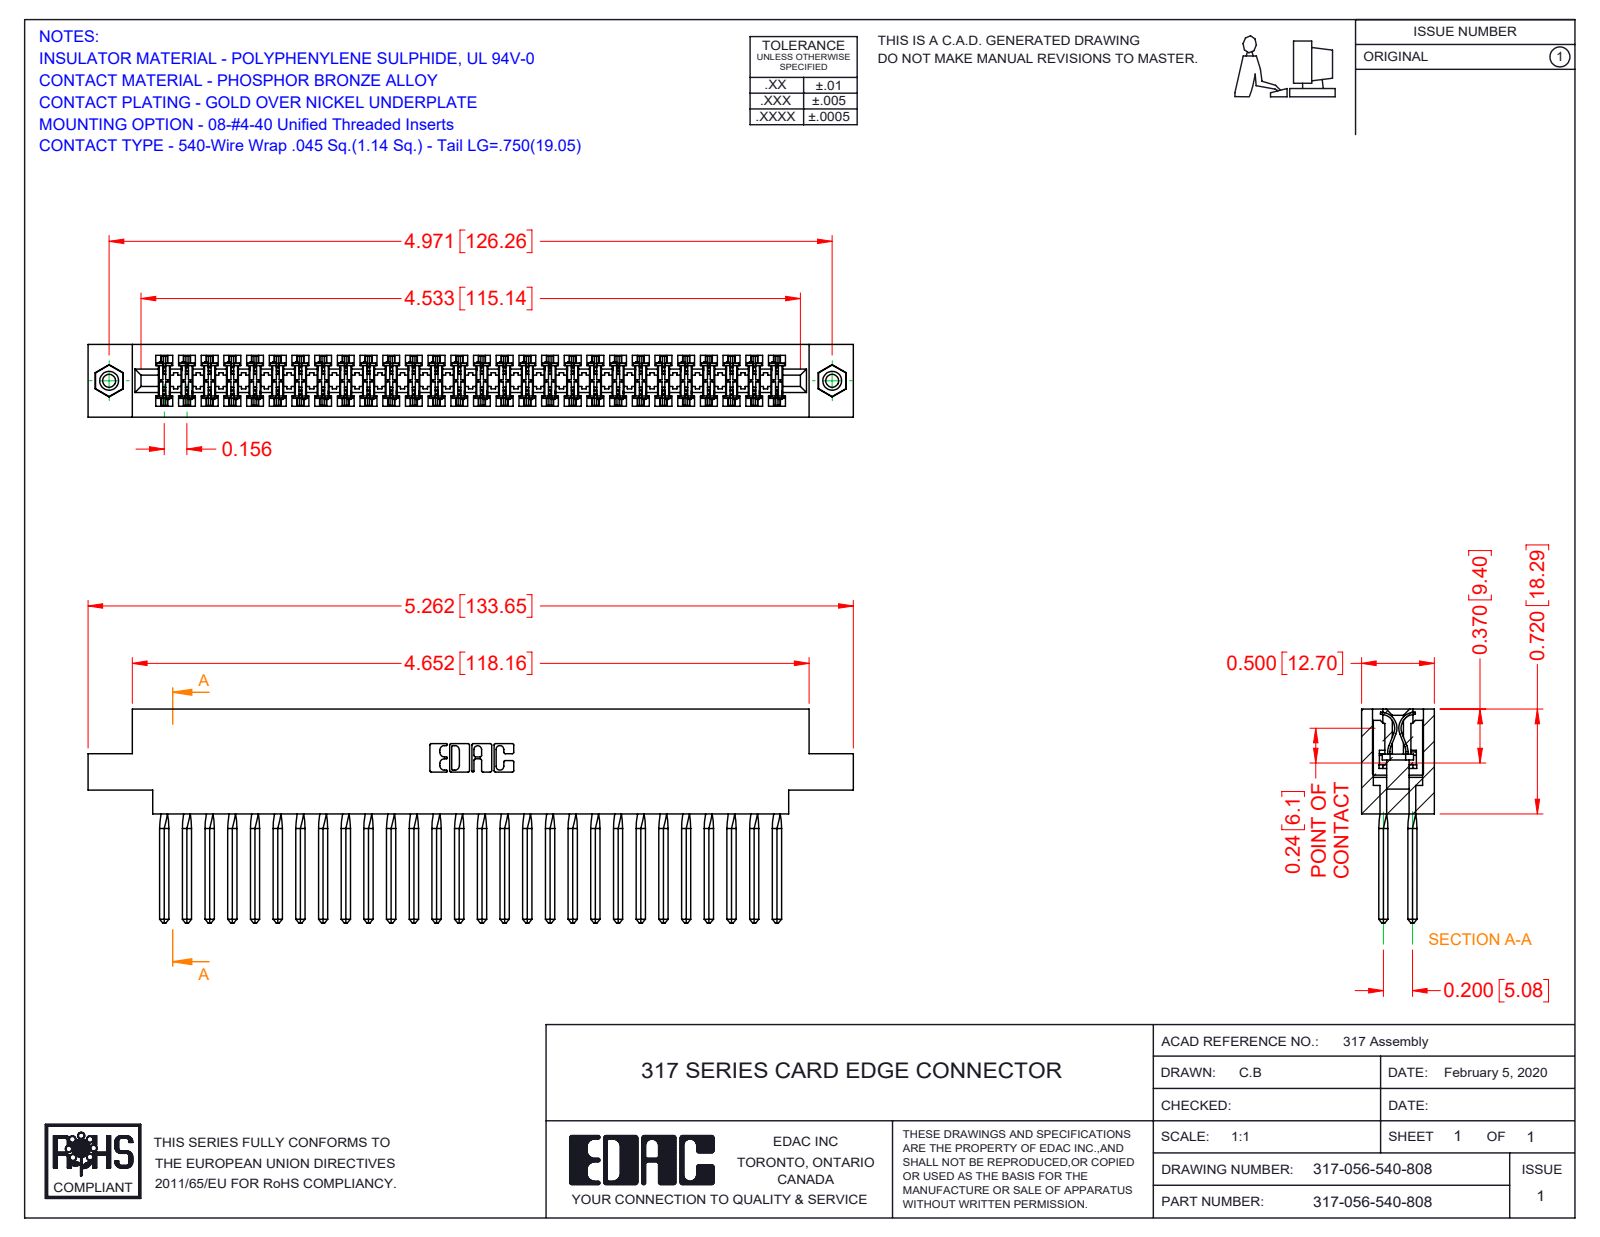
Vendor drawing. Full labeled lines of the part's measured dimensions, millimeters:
Part name (STEP PRODUCT): 317 Part_.156 Dia - TI; 317-290-001_540; 345-250-001_345-250-003-102; 317-056-540-808
STEP written by: SolidWorks 2016 (CONFIG_CONTROL_DESIGN)
Units: millimetres
Bodies: 59 solids, 5146 faces (4178 planar, 728 cylindrical, 240 other)
Overall size (bounding box): 133.7 × 37.3 × 12.7
Volume: 21 960 mm³ · Surface area: 32 220 mm²
Round holes (diameter × count): ⌀2.3 ×2, ⌀3.2 ×2, ⌀4 ×2
Round bosses / shafts (diameter × count): ⌀3.9 ×2
Partial cylindrical surfaces — rounded edges, fillets, slot ends (radius × count): R0.4 ×112, R0.3 ×22, R0.2 ×6, R0.8 ×6, R0.7 ×3, R2.4 ×2, R2.5 ×2, R2.8 ×2
Main face-to-face distances: 12.7, 1.9, 10.8, 8.9, 2.8, 5, 2.4, 5.1, 18.3, 2.9
Hole centre spacings: 126.3
